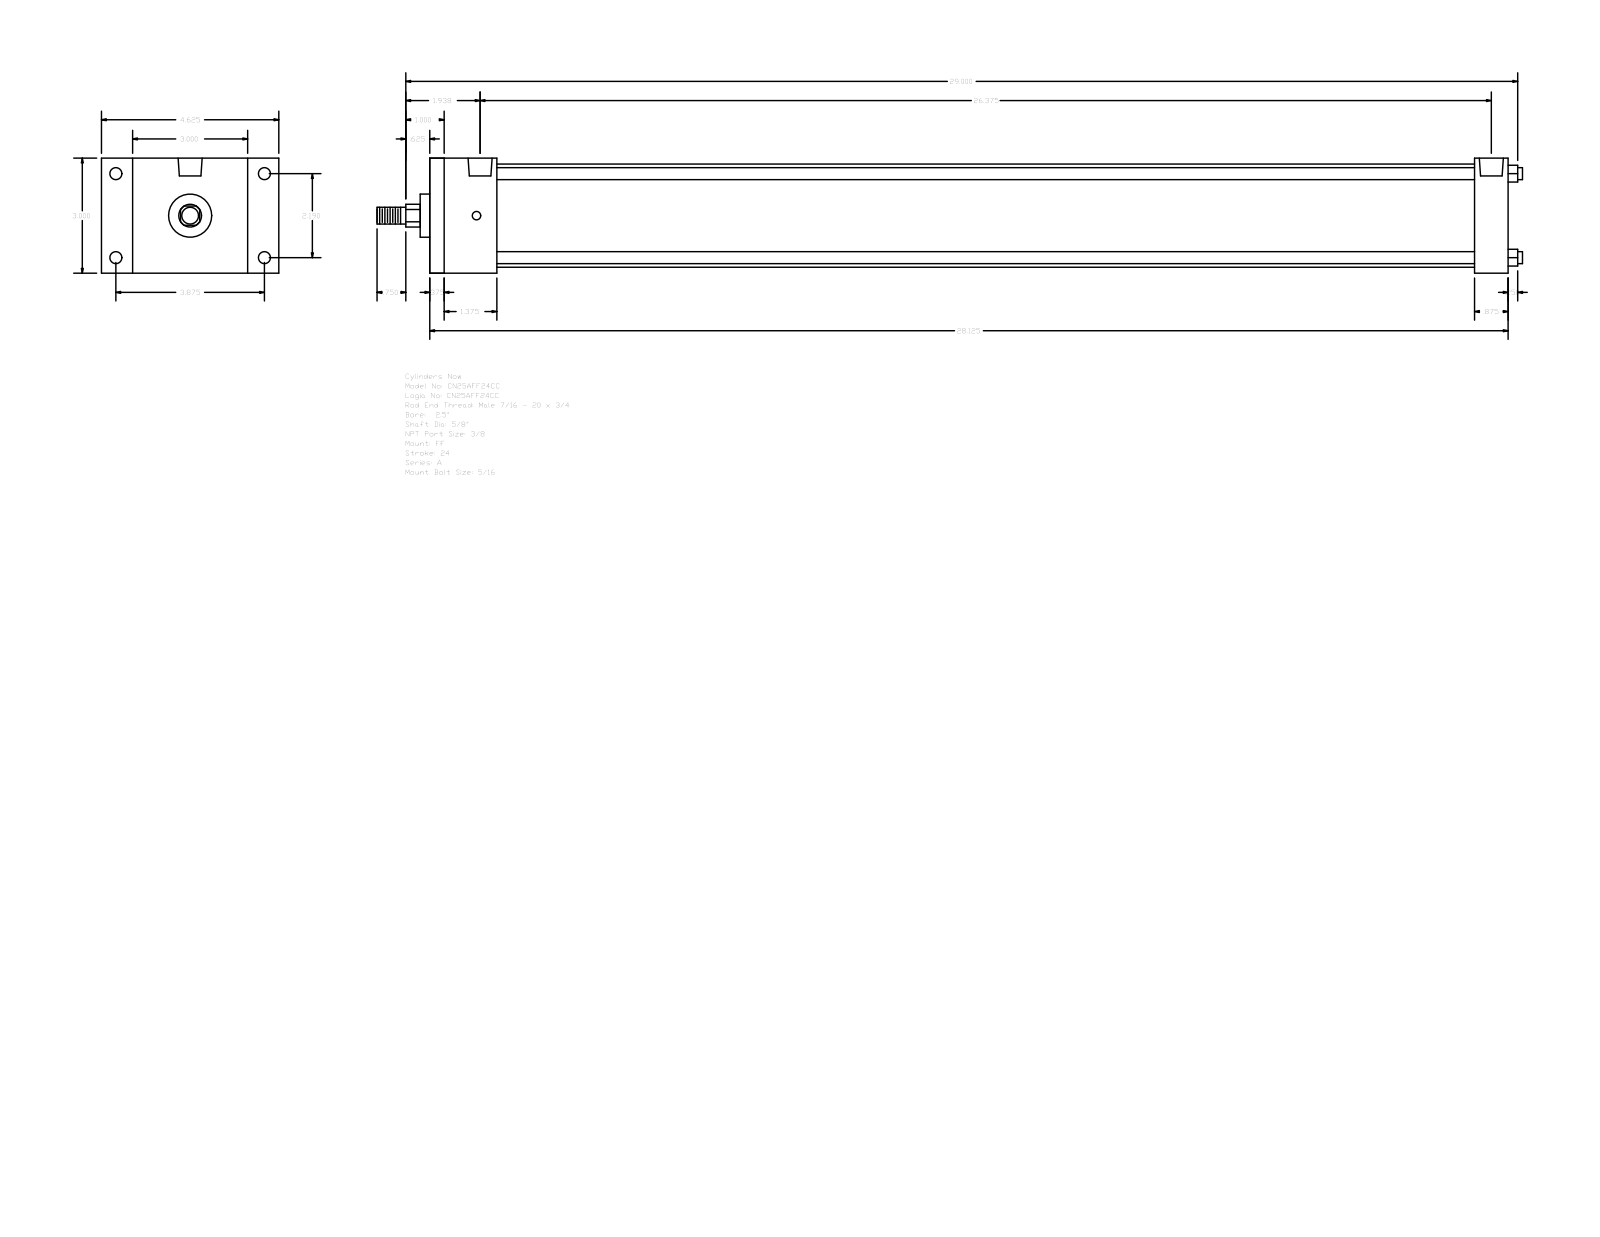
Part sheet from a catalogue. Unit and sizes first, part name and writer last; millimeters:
Units: millimetres
Overall size (bounding box): 758.83 × 117.47 × 76.2
Round holes (diameter × count): ⌀5.56 ×4, ⌀7.94 ×4, ⌀15.93 ×2
Round bosses / shafts (diameter × count): ⌀7.94 ×4, ⌀68.33 ×1, ⌀28.57 ×1, ⌀15.88 ×1, ⌀11.11 ×1
Partial cylindrical surfaces — rounded edges, fillets, slot ends (radius × count): R7.54 ×1
Main face-to-face distances: 76.2, 714.37, 9.52, 704.85, 44.45, 34.93, 692.14, 682.62, 647.69, 669.92
Hole centre spacings: 2.38, 55.62, 98.42, 113.05, 672.31, 674.69, 669.93
Bodies: 0 solids, 92 faces (64 planar, 28 cylindrical, 0 other)
Part name (STEP PRODUCT): A_FF__0250_0.625
STEP written by: GSSL Pune (CONFIG_CONTROL_DESIGN)
